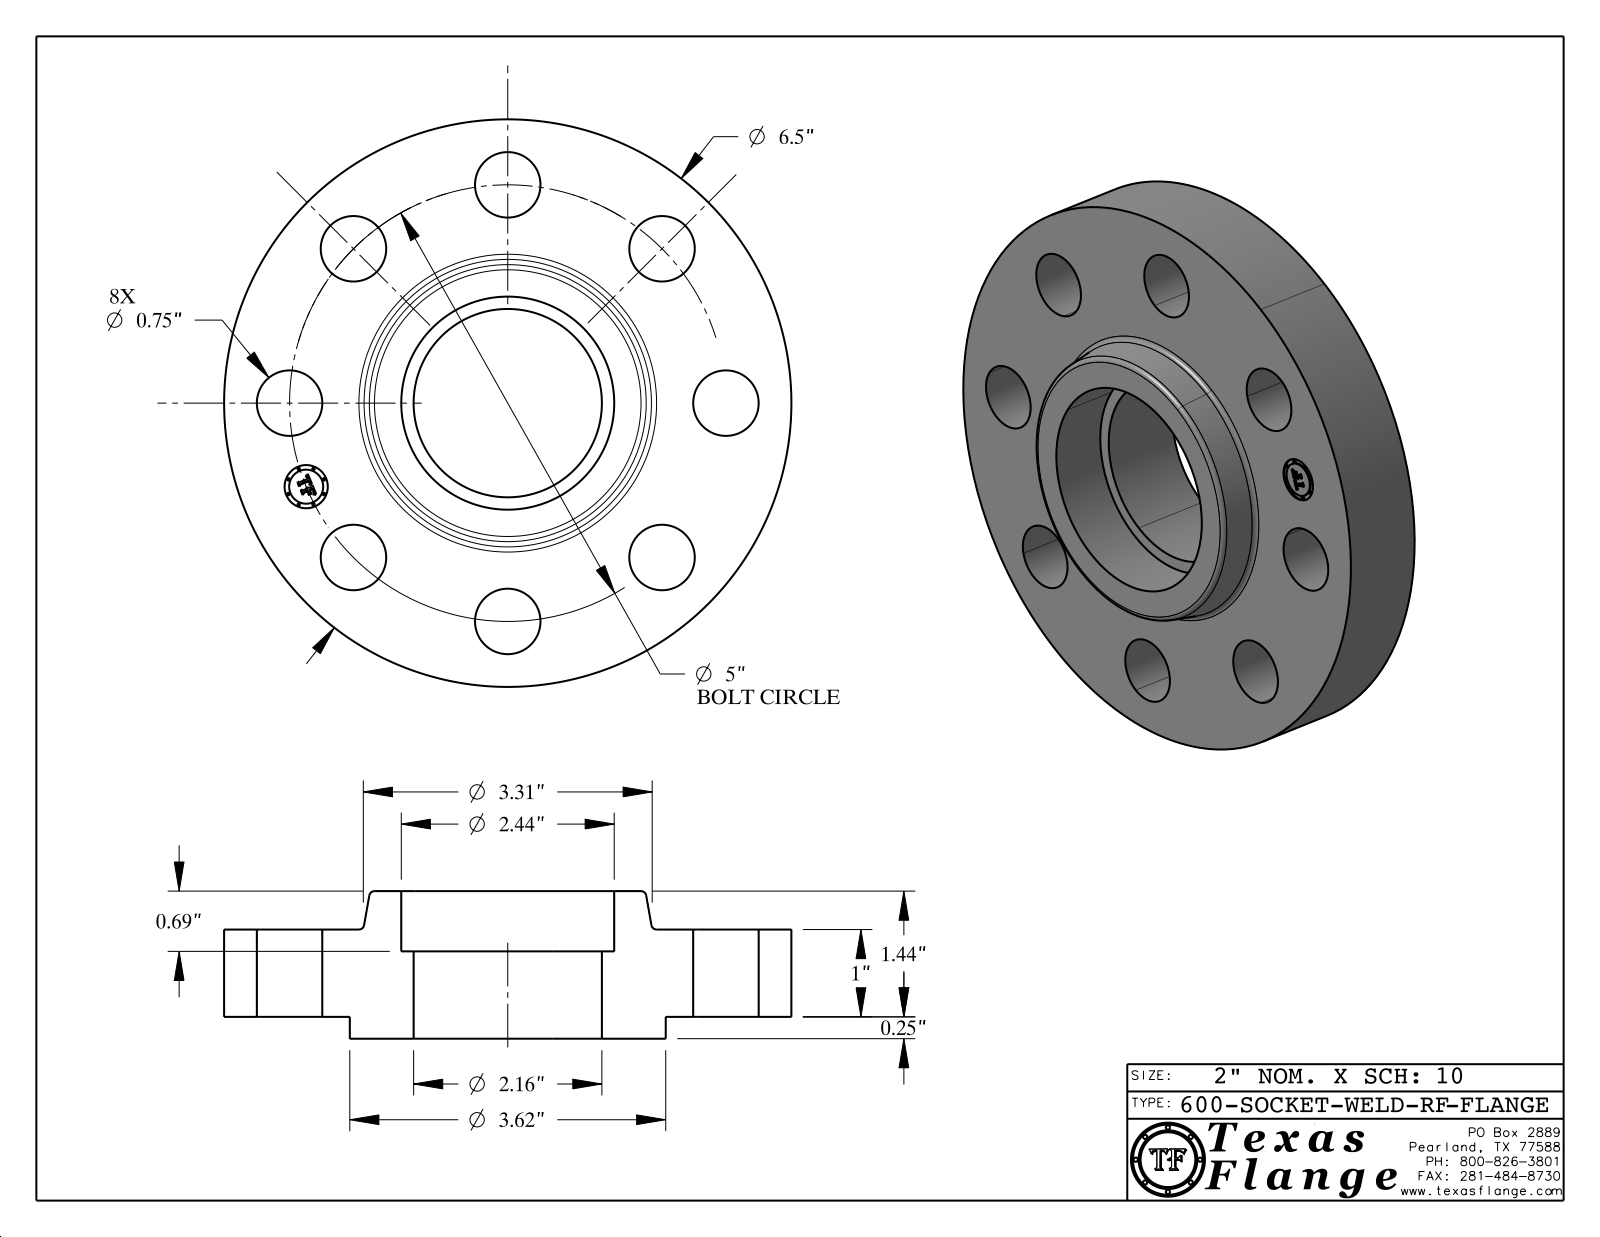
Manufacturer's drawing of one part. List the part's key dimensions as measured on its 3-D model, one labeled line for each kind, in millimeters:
Part name (STEP PRODUCT): 600-SOCKET-WELD-RF
STEP written by: CATIA V5 STEP AP214 (AUTOMOTIVE_DESIGN)
Units: millimetres
Bodies: 1 solid, 420 faces (370 planar, 44 cylindrical, 6 other)
Overall size (bounding box): 165.1 × 165.1 × 42.9
Volume: 474 400 mm³ · Surface area: 70 770 mm²
Round holes (diameter × count): ⌀19.1 ×8, ⌀12.6 ×1, ⌀54.8 ×1, ⌀62 ×1
Round bosses / shafts (diameter × count): ⌀0.8 ×8, ⌀165.1 ×1, ⌀91.9 ×1, ⌀9.9 ×1
Main face-to-face distances: 25.4, 6.4, 31.8, 42.9, 36.6, 11.2, 19.1, 17.5, 31.4, 25
Hole centre spacings: 63.5, 48.6, 89.8, 117.3, 127, 24.8, 70.6, 105.6
